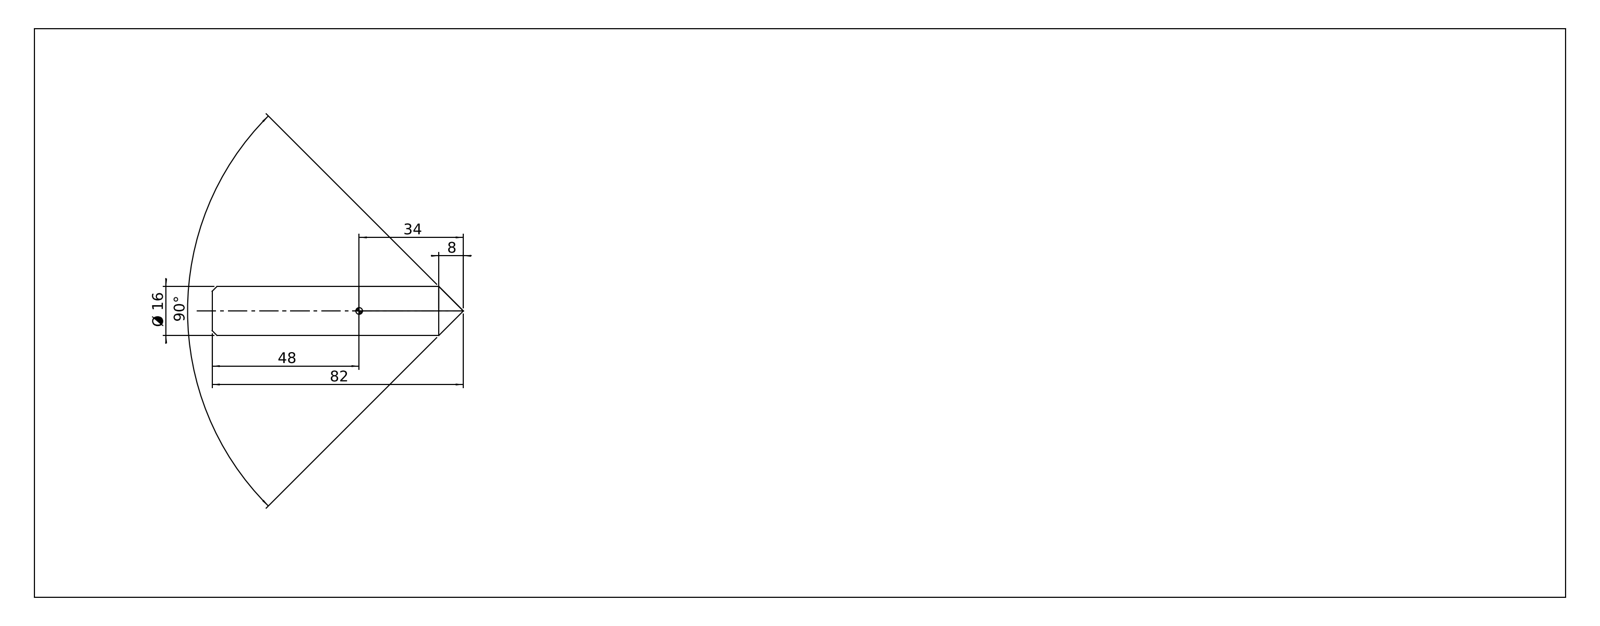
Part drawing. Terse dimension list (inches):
name: 890.160.00
written by: SolidWorks 2019 (CONFIG_CONTROL_DESIGN)
unit: in
bodies: 2 solids, 6 faces (3 planar, 1 cylindrical, 2 other)
size: 3.228 × 0.63 × 0.63
volume: 0.937 in³; area: 7.063 in²
bosses: 1× ⌀0.63
face distances: 2.913
